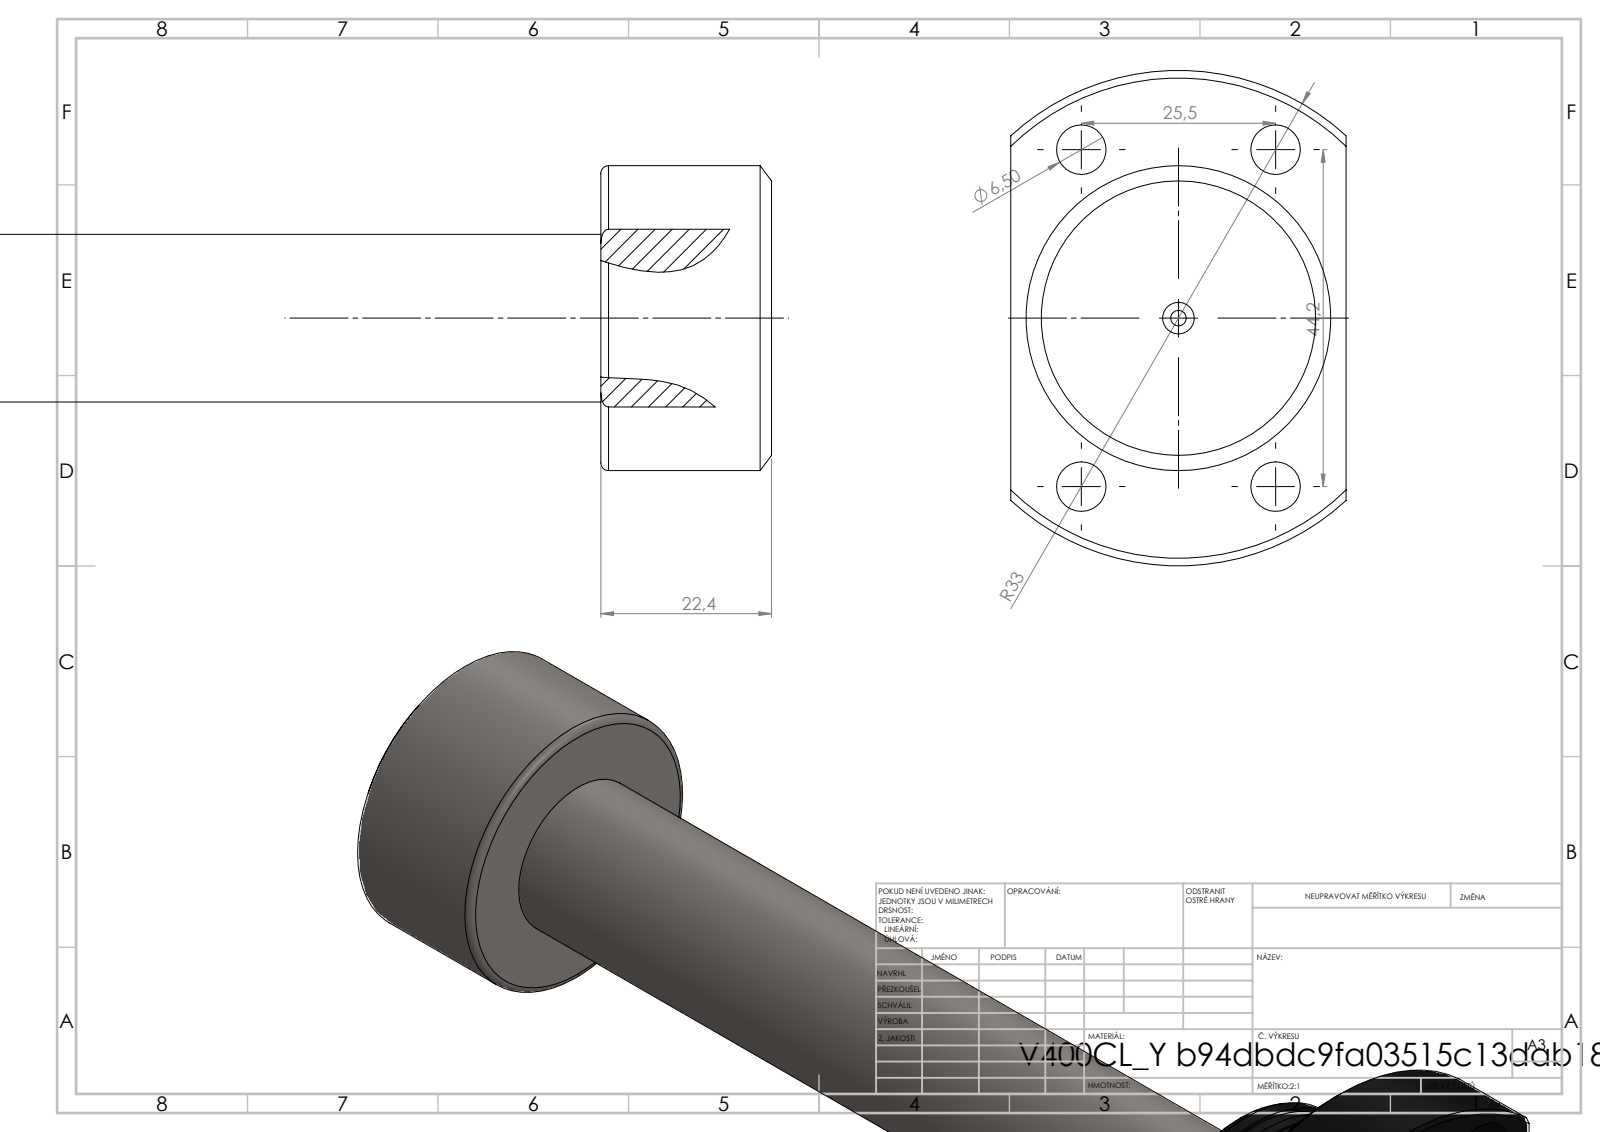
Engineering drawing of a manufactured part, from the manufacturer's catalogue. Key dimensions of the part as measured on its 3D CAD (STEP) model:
Part name (STEP PRODUCT): V400CL_VC_X; V400CL_PC_Y; MTA
STEP written by: SolidWorks 2019 (CONFIG_CONTROL_DESIGN)
Units: millimetres
Bodies: 3 solids, 152 faces (41 planar, 51 cylindrical, 60 other)
Overall size (bounding box): 220 × 65 × 44
Volume: 141 678 mm³ · Surface area: 32 477 mm²
Round holes (diameter × count): ⌀6.5 ×4, ⌀10.5 ×4, ⌀2.05 ×1, ⌀5 ×1, ⌀6 ×1, ⌀22 ×1, ⌀26.5 ×1
Round bosses / shafts (diameter × count): ⌀40 ×1, ⌀39 ×1, ⌀14 ×1, ⌀12 ×1
Partial cylindrical surfaces — rounded edges, fillets, slot ends (radius × count): R10.75 ×1, R32.5 ×1
Main face-to-face distances: 14, 162.95, 176.95, 22.4, 140.55, 154.55, 145.45, 123.05, 17.5, 31.5
Hole centre spacings: 25.51, 25.5, 44.2, 51.03
